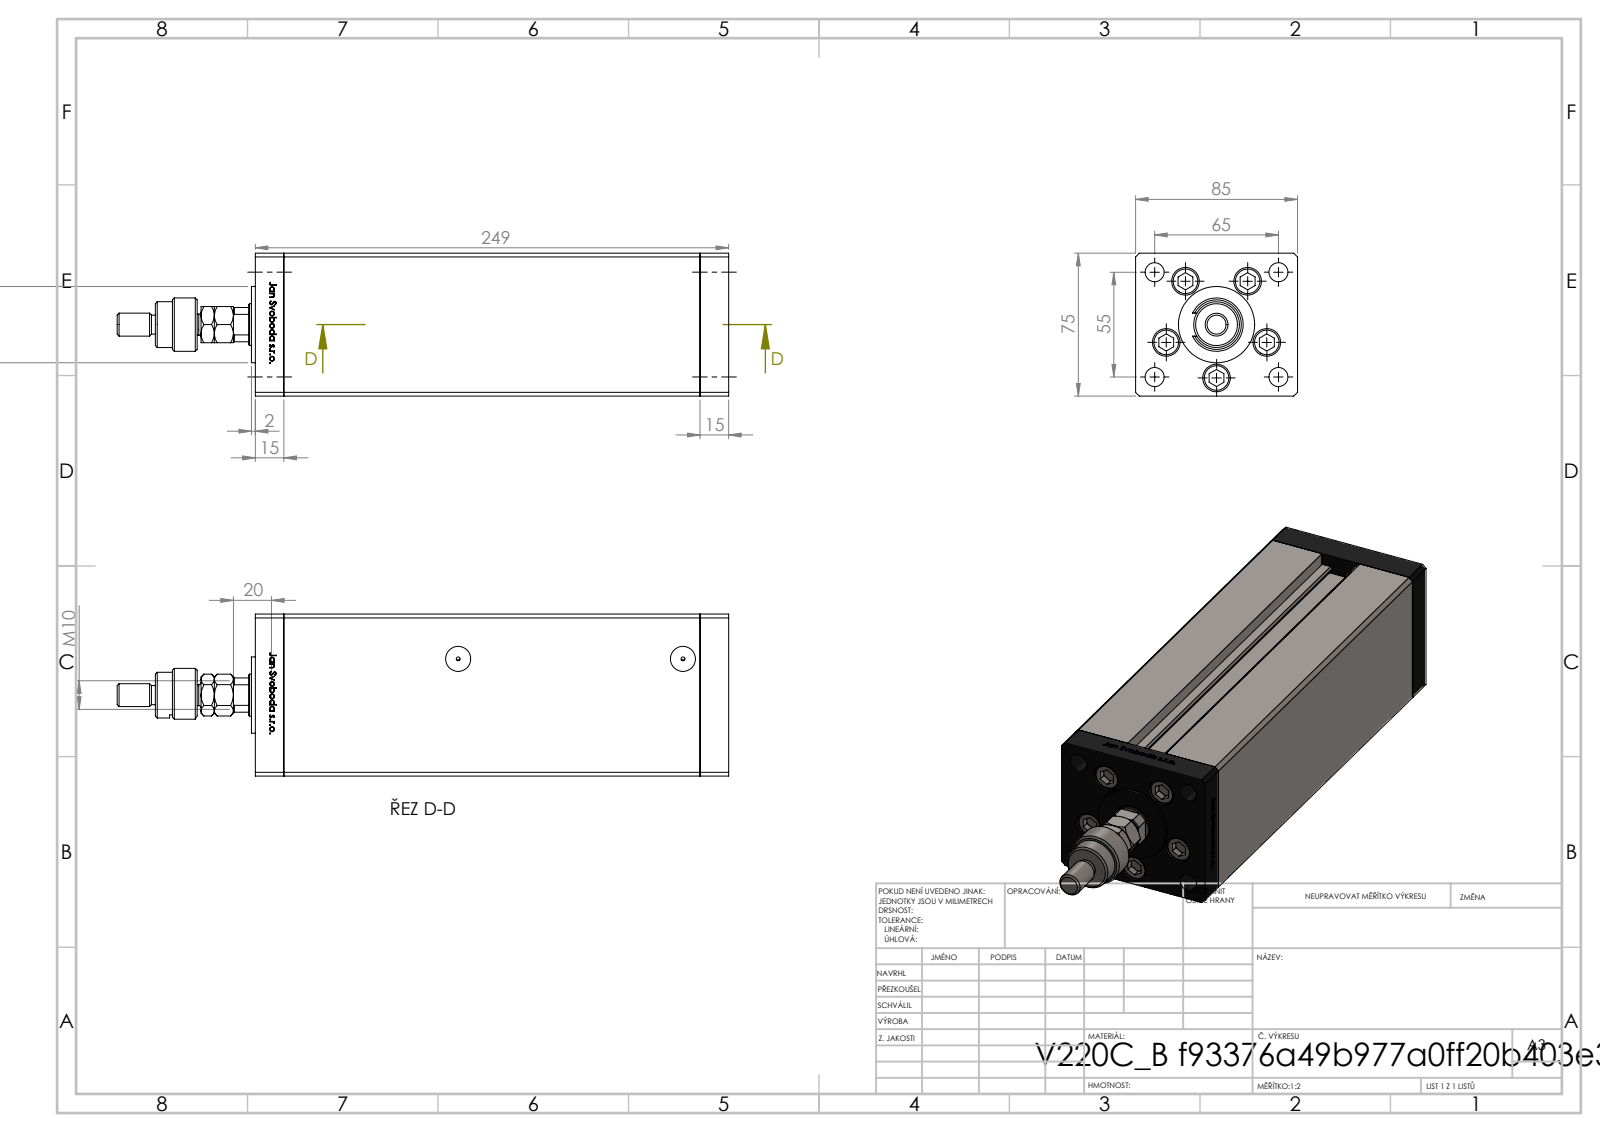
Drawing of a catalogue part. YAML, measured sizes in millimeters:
part_name: "V220C BACK_B; FEMALE_PART_FOR_DFA; MFA; ALLEN BOLT (+3 more)"
step_written_by: "SolidWorks 2019 (CONFIG_CONTROL_DESIGN)"
units: millimeters
bodies: {solids: 16, faces: 1270, planar: 492, cylindrical: 160, other: 618}
overall_size: [321, 85, 75]
volume: 1400000
surface_area: 205024
round_holes:
  - {diameter: 11, count: 5}
  - {diameter: 14.5, count: 5}
  - {diameter: 10, count: 4}
  - {diameter: 2, count: 2}
  - {diameter: 13.16, count: 2}
  - {diameter: 13.5, count: 1}
  - {diameter: 22, count: 1}
round_bosses_or_shafts:
  - {diameter: 8, count: 5}
  - {diameter: 40, count: 1}
  - {diameter: 28, count: 1}
  - {diameter: 24, count: 1}
  - {diameter: 18, count: 1}
  - {diameter: 12, count: 1}
  - {diameter: 11, count: 1}
  - {diameter: 10, count: 1}
partial_cylinders:
  - {radius: 0.93, count: 2}
  - {radius: 9.75, count: 1}
  - {radius: 10.5, count: 1}
face_to_face_distances: [85, 75, 15, 218.5, 233.5, 248.5, 34.25, 68.5, 64.5, 10.5]
hole_center_spacings: [28, 42.57, 16.86, 19.17, 32.33, 32.5, 33.63, 37.33]
